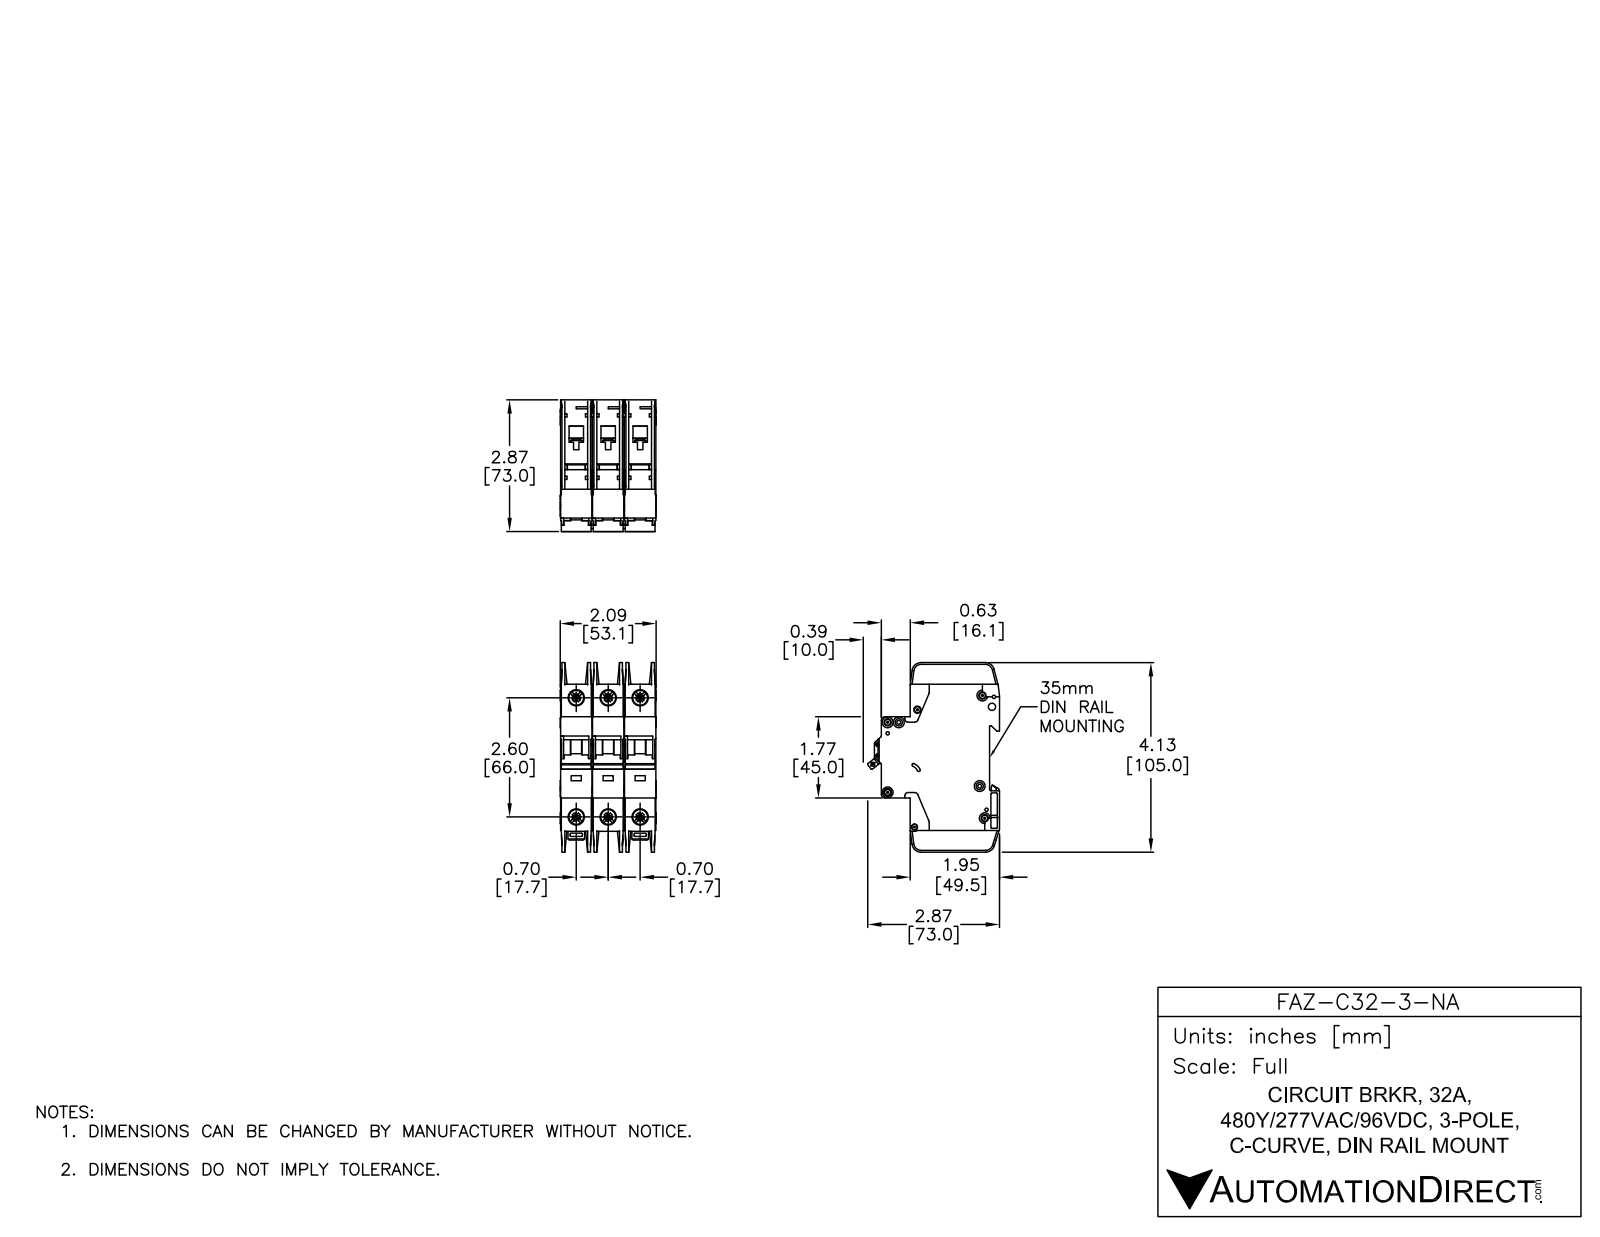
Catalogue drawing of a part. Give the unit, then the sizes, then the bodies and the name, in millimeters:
Units: millimetres
Overall size (bounding box): 105 × 73.04 × 53.1
Round holes (diameter × count): ⌀3.6 ×7, ⌀7.15 ×6, ⌀8.2 ×6, ⌀1.09 ×2, ⌀1.5 ×2, ⌀4 ×2, ⌀1.9 ×1, ⌀2.15 ×1, ⌀2.2 ×1, ⌀2.55 ×1, ⌀3.3 ×1, ⌀3.4 ×1
Round bosses / shafts (diameter × count): ⌀6 ×7, ⌀2.5 ×3
Partial cylindrical surfaces — rounded edges, fillets, slot ends (radius × count): R0.25 ×65, R0.5 ×30, R1 ×26, R2 ×14, R1.8 ×5, R5 ×5, R4 ×4, R0.2 ×2
Main face-to-face distances: 17.7, 35.4, 17.5, 35.2, 0.7, 15.05, 2.45, 1.75, 15.75, 13.3
Hole centre spacings: 17.7, 68.33, 66, 6.2, 35.4, 74.89, 5.19, 6.1
Volume: 233 085 mm³ · Surface area: 74 219 mm²
Bodies: 9 solids, 2352 faces (1227 planar, 789 cylindrical, 336 other)
Part name (STEP PRODUCT): FAZ-C32-3-NA
STEP written by: SolidWorks 2014 (AUTOMOTIVE_DESIGN)
